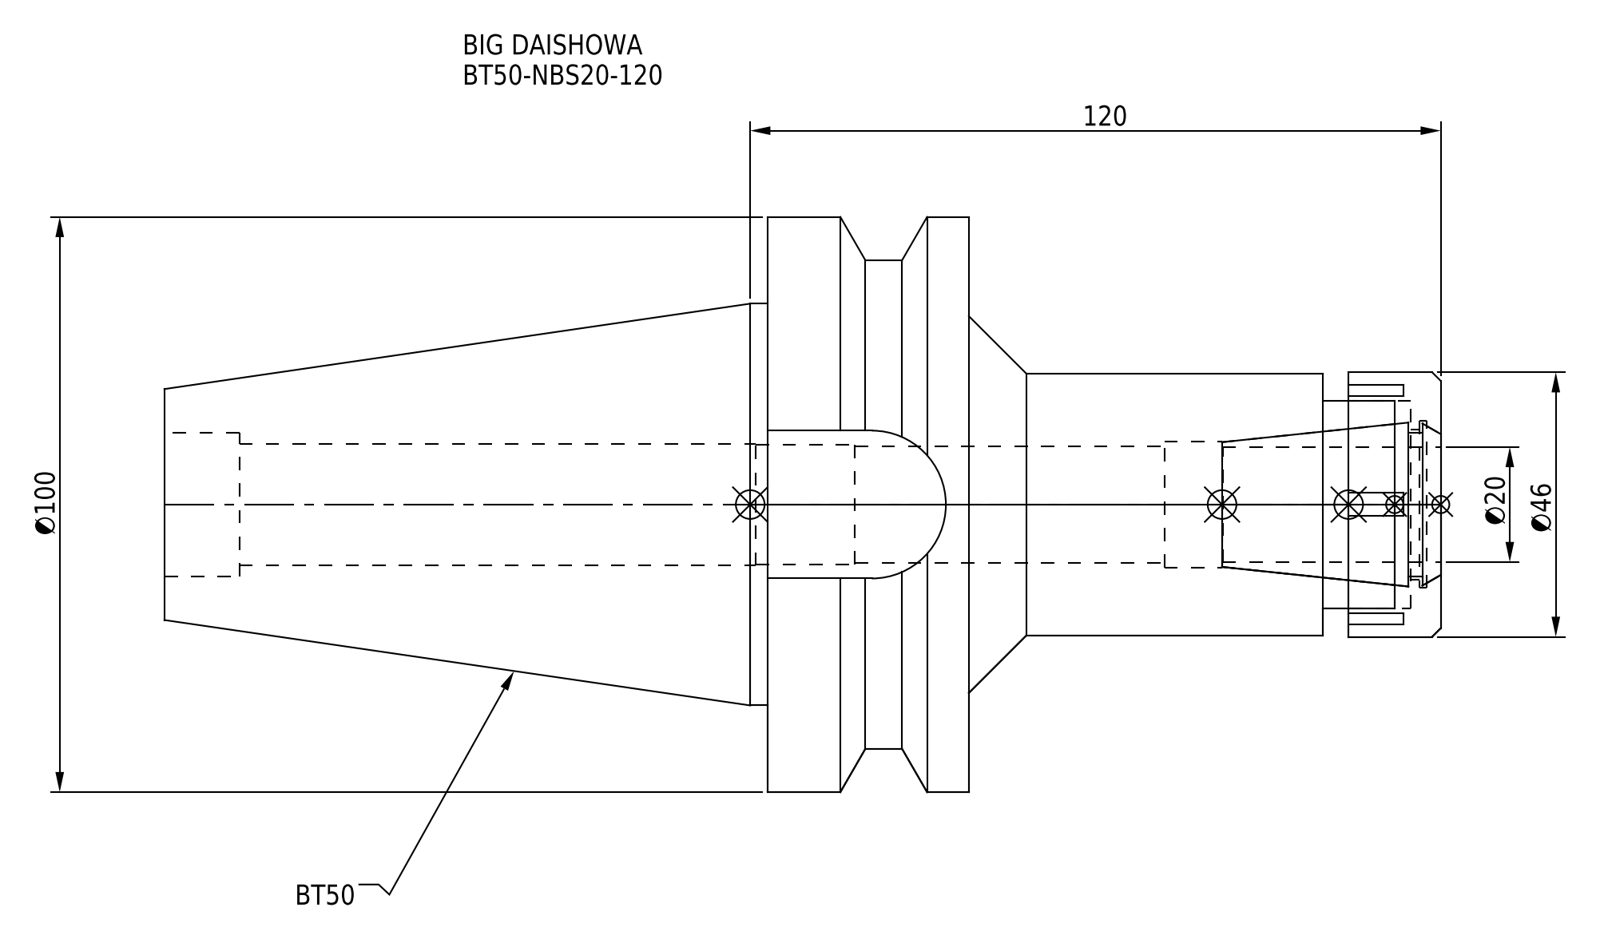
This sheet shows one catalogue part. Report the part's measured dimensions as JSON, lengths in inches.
{"part_name": "NBN20_1.stp; DXF_TEMP_ASSY_ASM_4_ASM.stp; BT50NB20120-200_ASM.stp; BT50-NBS20-120-FreeParts (+3 more)", "step_written_by": "SolidWorks 2019 (CONFIG_CONTROL_DESIGN)", "units": "inches", "bodies": {"solids": 2, "faces": 93, "planar": 45, "cylindrical": 34, "other": 14}, "overall_size": [8.732, 3.937, 3.937], "volume_in3": 33.38, "surface_area_in2": 116.4, "round_holes": [[0.799, 1], [0.819, 1], [0.835, 1], [0.866, 1], [0.984, 1], [1.024, 1], [1.142, 1], [1.417, 1]], "round_bosses_or_shafts": [[3.937, 1], [3.346, 1], [2.75, 1], [1.811, 1], [1.791, 1]], "partial_cylinders_radius": [[0.506, 1]], "face_to_face_distances": [1.378, 3.228, 4.606, 0.315, 8.732, 5.504, 4.126, 2.787, 0.807, 2.421]}
